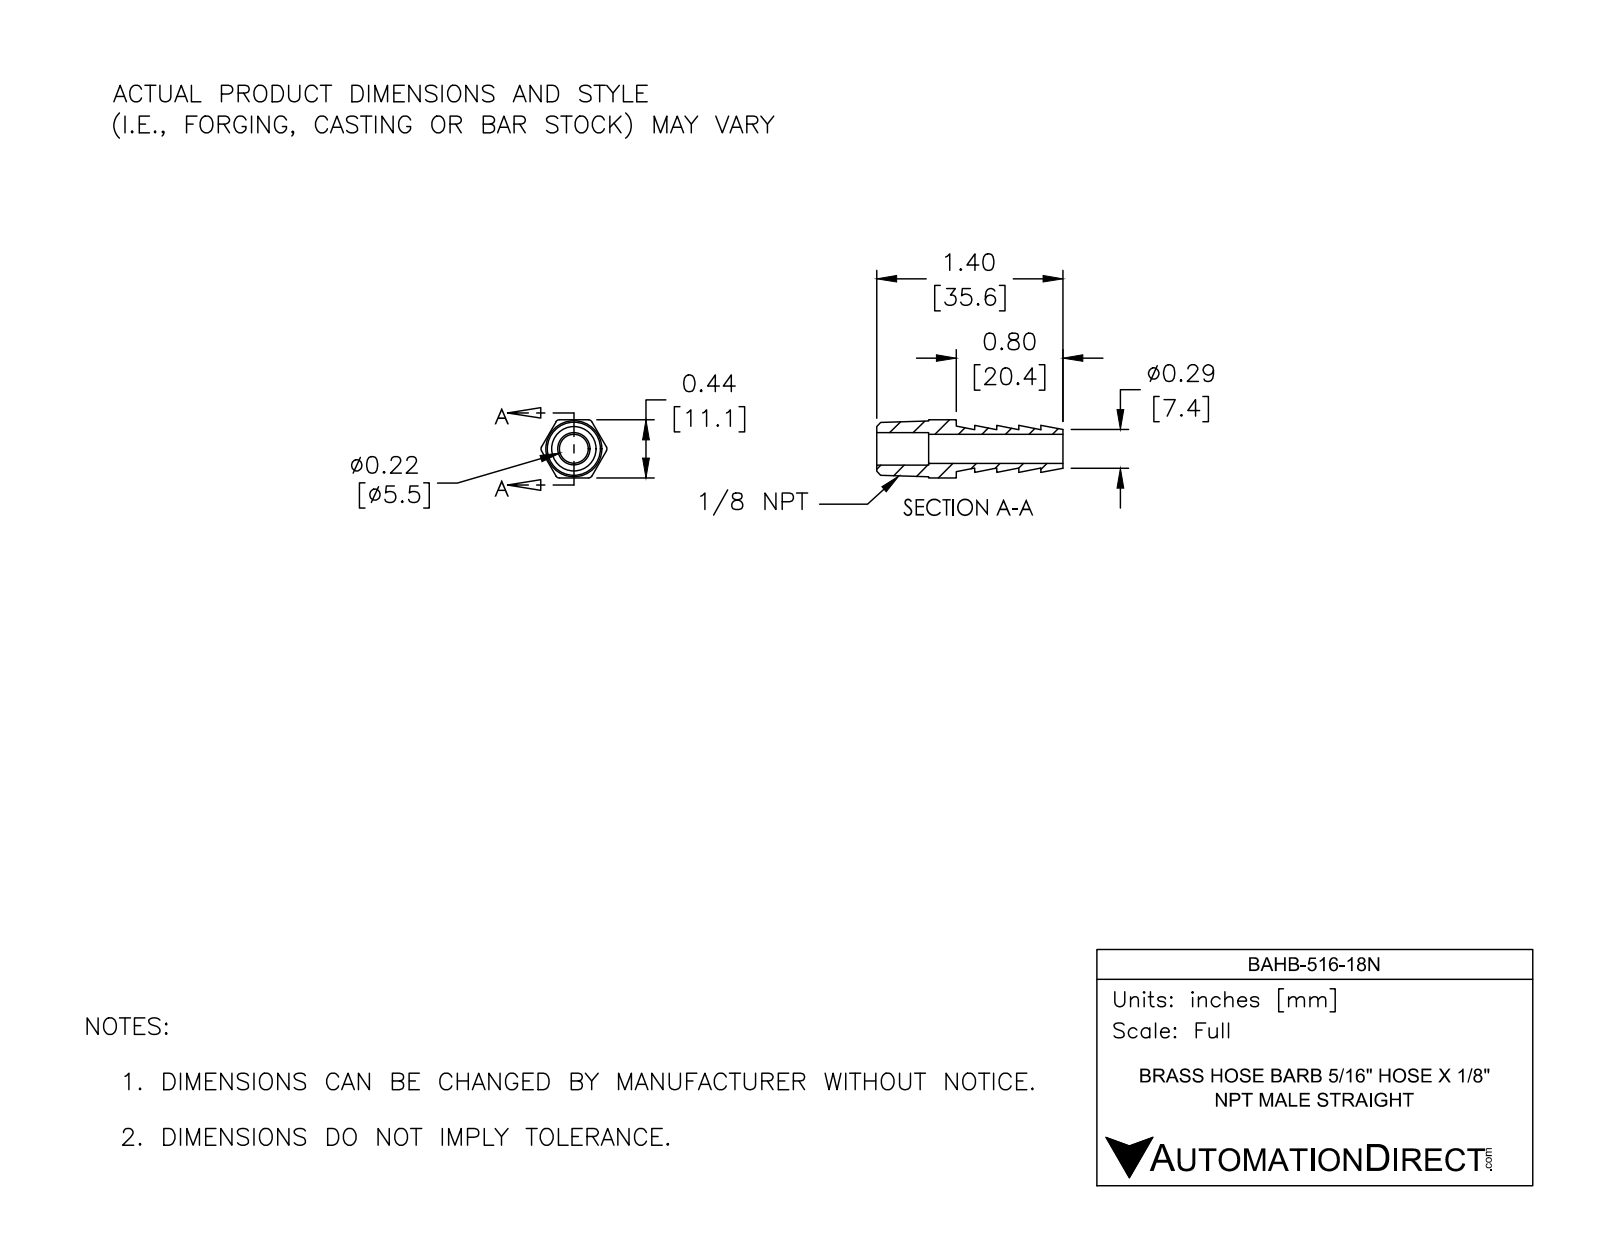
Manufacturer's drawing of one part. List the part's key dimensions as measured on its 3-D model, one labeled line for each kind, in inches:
Part name (STEP PRODUCT): BAHB-516-18N
STEP written by: SolidWorks 2017 (AUTOMOTIVE_DESIGN)
Units: inches
Bodies: 1 solid, 39 faces (15 planar, 10 cylindrical, 14 other)
Overall size (bounding box): 1.402 × 0.496 × 0.438
Volume: 0.094 in³ · Surface area: 2.953 in²
Round holes (diameter × count): ⌀0.218 ×1, ⌀0.244 ×1
Partial cylindrical surfaces — rounded edges, fillets, slot ends (radius × count): R0.03 ×6
Main face-to-face distances: 0.438, 0.166, 0.332, 0.498, 0.599, 0.208, 0.391, 0.637, 0.845, 1.236
